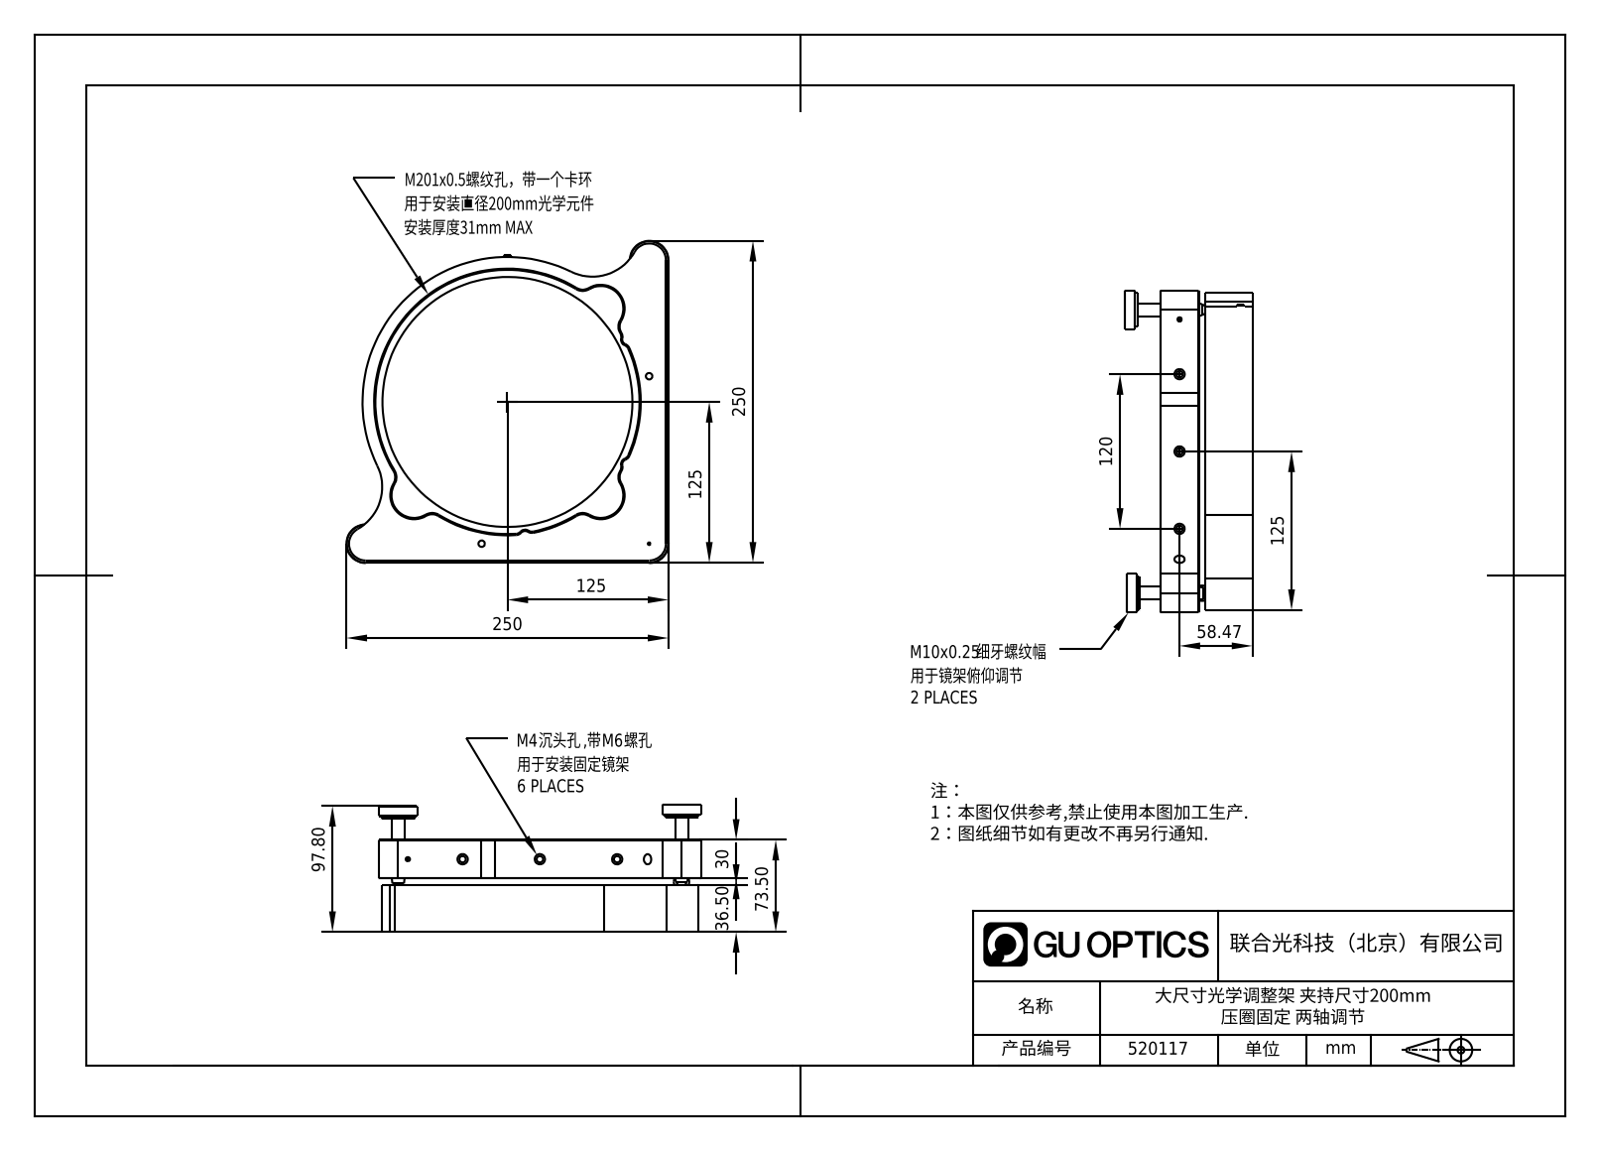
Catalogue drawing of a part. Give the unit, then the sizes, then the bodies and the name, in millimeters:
Units: millimetres
Overall size (bounding box): 250 × 250 × 97.75
Round holes (diameter × count): ⌀3.3 ×8, ⌀5 ×8, ⌀8 ×6, ⌀9 ×6, ⌀15 ×3, ⌀2 ×2, ⌀7 ×2, ⌀13 ×2, ⌀20.5 ×2, ⌀196 ×1, ⌀196.7 ×1, ⌀200.5 ×1
Round bosses / shafts (diameter × count): ⌀30 ×2, ⌀26 ×2, ⌀10 ×2, ⌀201 ×1, ⌀20.3 ×1, ⌀20 ×1, ⌀10.2 ×1, ⌀6 ×1
Partial cylindrical surfaces — rounded edges, fillets, slot ends (radius × count): R1.05 ×12, R2 ×4, R6 ×4, R30 ×4, R40 ×2, R10 ×1, R13 ×1, R15 ×1
Main face-to-face distances: 30, 36.5, 6.97, 43.47, 36.97, 73.47, 2, 28, 29.5, 1.5
Hole centre spacings: 60, 130, 95, 35, 42.5, 102.5, 155.56, 162.5
Bodies: 0 solids, 346 faces (115 planar, 164 cylindrical, 67 other)
STEP written by: SolidWorks 2021 (CONFIG_CONTROL_DESIGN)
